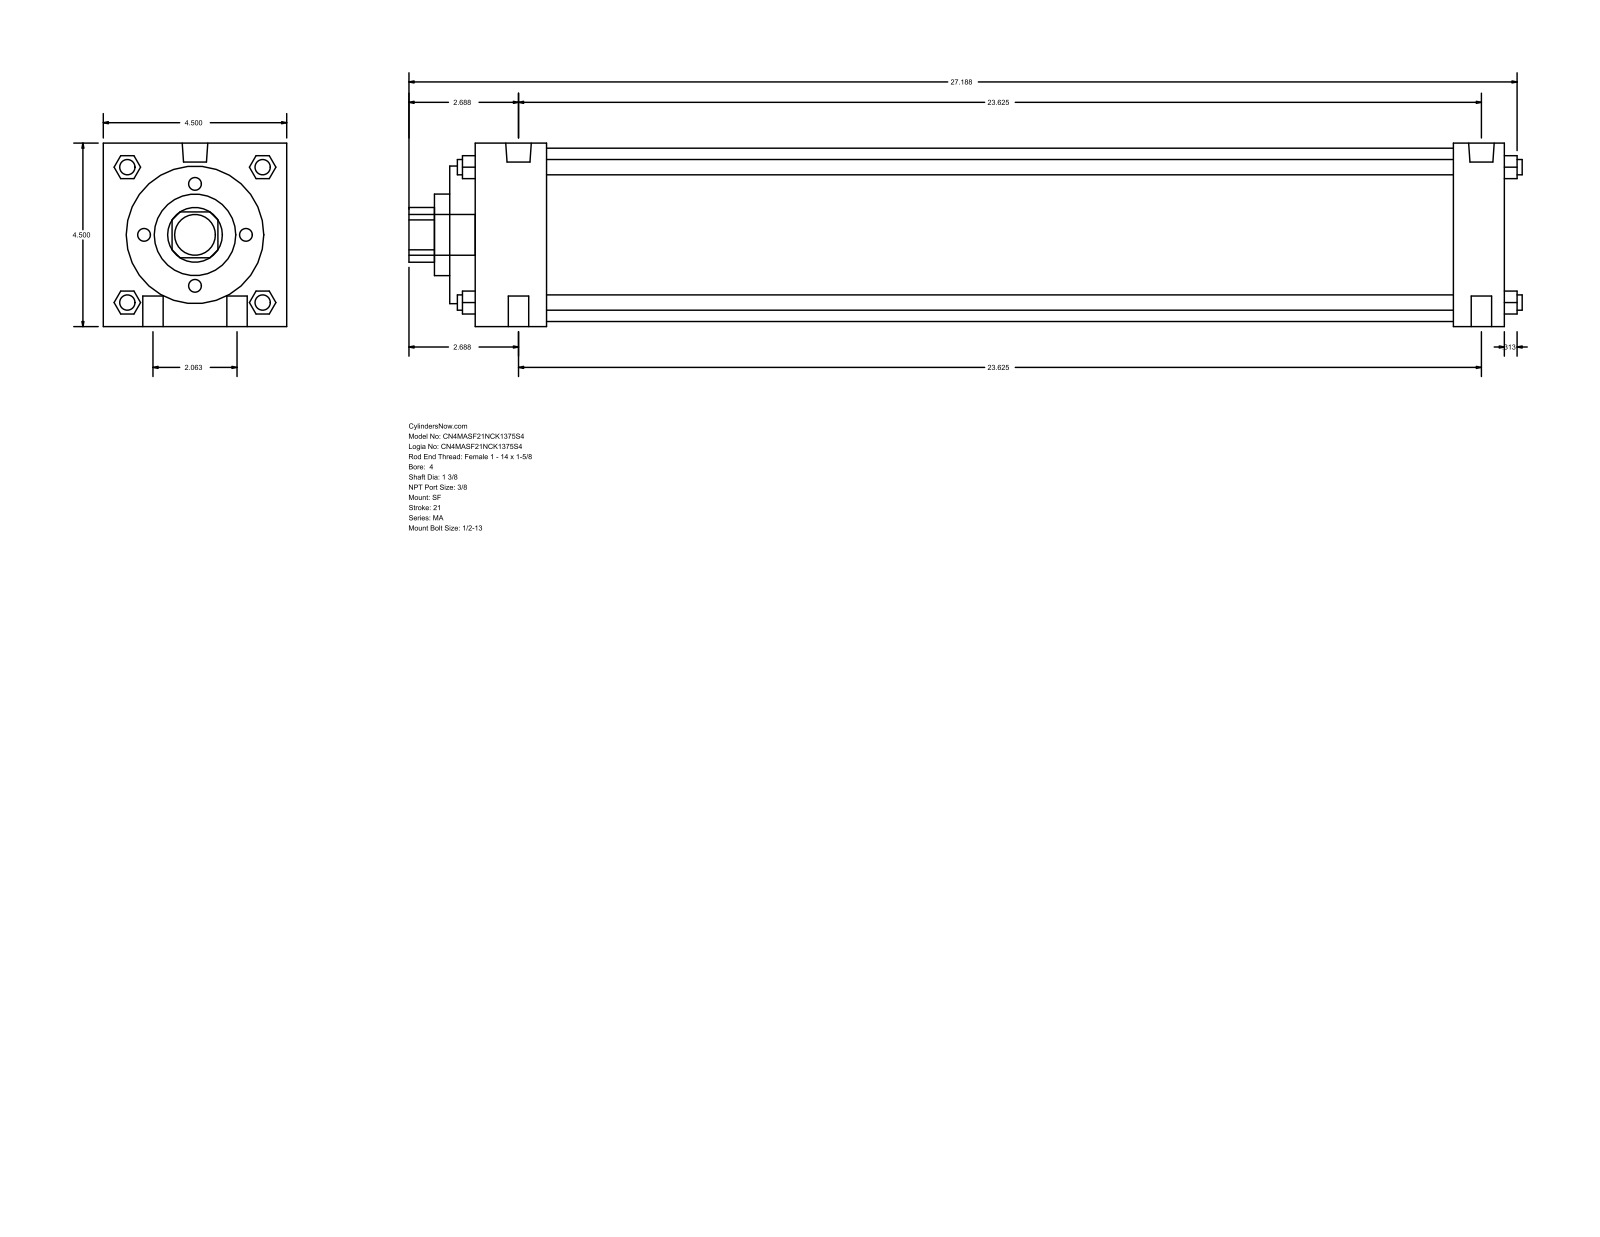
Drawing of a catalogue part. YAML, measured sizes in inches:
part_name: "MA_SF__0400_1.375"
step_written_by: "GSSL Pune (CONFIG_CONTROL_DESIGN)"
units: inches
bodies: {solids: 0, faces: 126, planar: 95, cylindrical: 31, other: 0}
overall_size: [27.313, 4.5, 4.5]
round_holes:
  - {diameter: 1.375, count: 1}
  - {diameter: 2, count: 1}
  - {diameter: 3.375, count: 1}
  - {diameter: 4.25, count: 1}
round_bosses_or_shafts:
  - {diameter: 0.5, count: 4}
  - {diameter: 0.375, count: 4}
  - {diameter: 0.627, count: 2}
  - {diameter: 0.437, count: 2}
  - {diameter: 1, count: 1}
partial_cylinders:
  - {radius: 0.672, count: 1}
face_to_face_distances: [4.5, 25.25, 25.875, 0.625, 24.625, 24, 1.25, 2.375, 1.75, 22.25]
